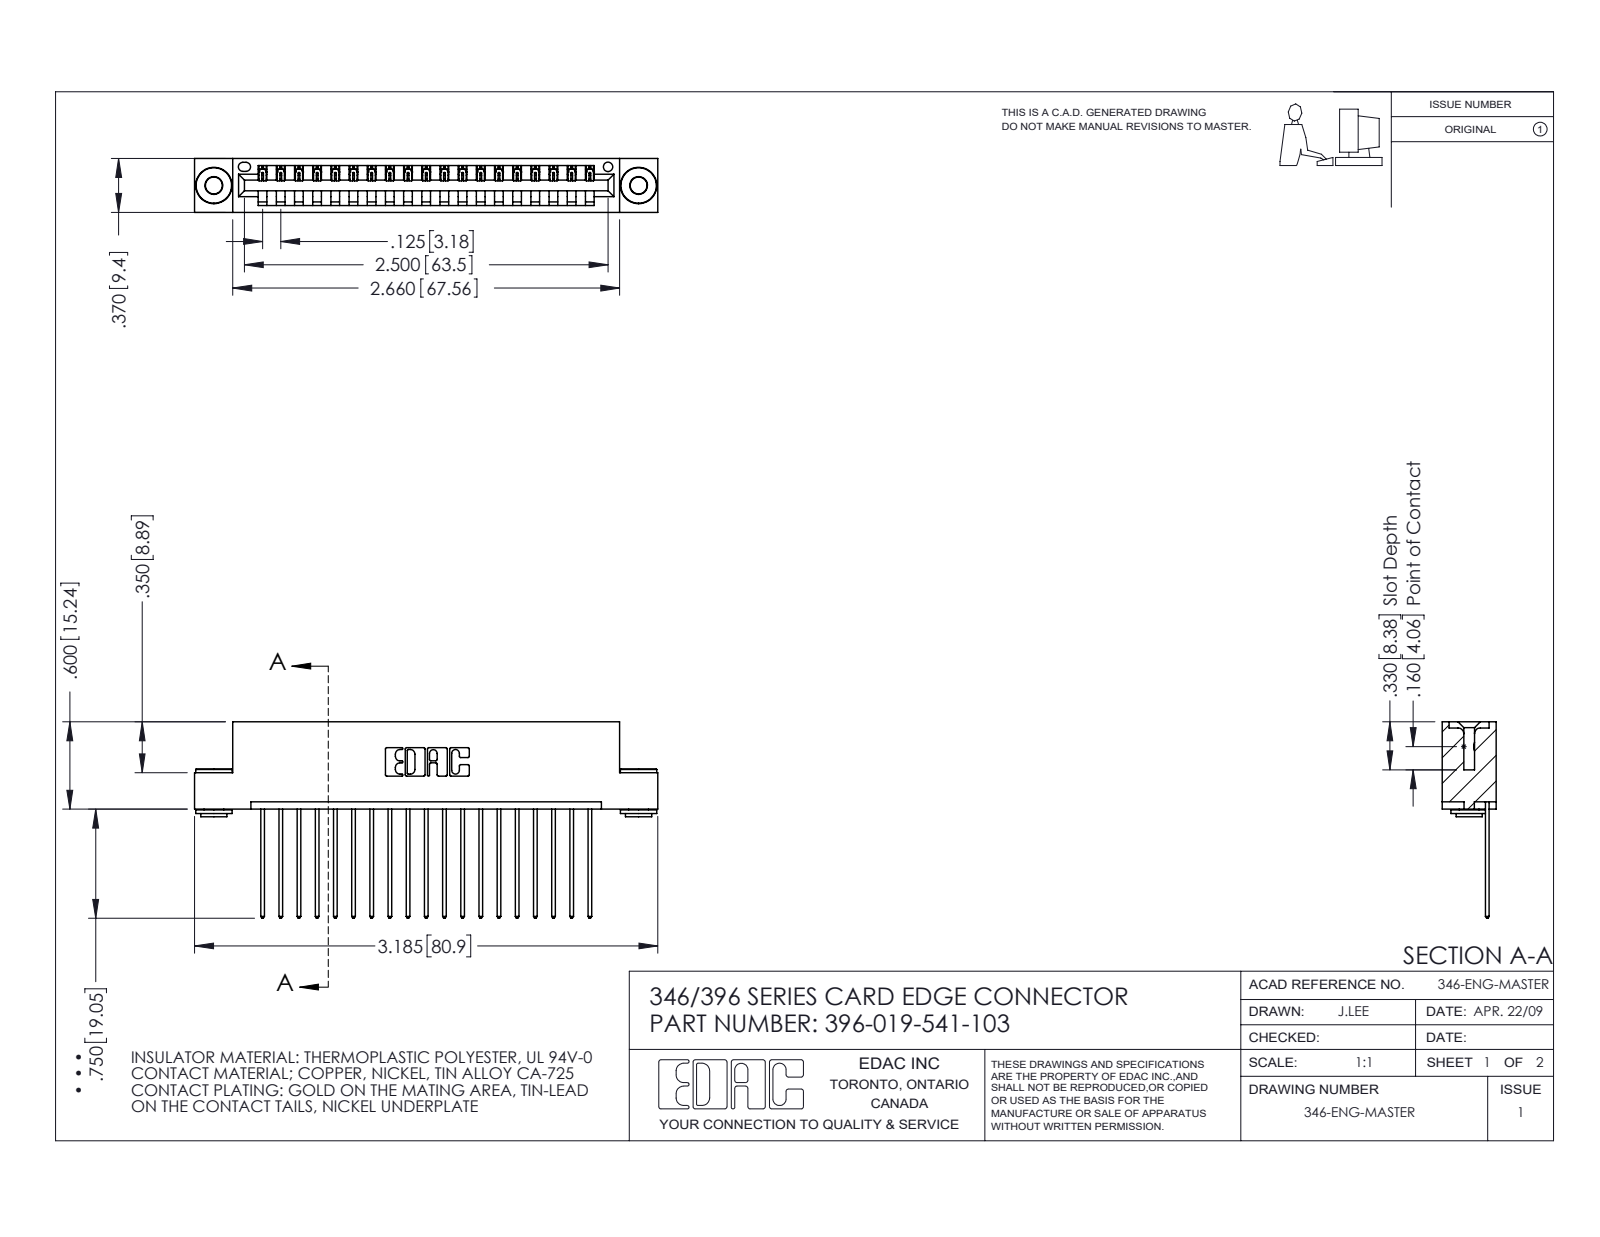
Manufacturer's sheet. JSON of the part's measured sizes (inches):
{"part_name": "345-292-001_345-293-141; 396-019-541-103; 346 Part_Flush Mounting Lugs - 0.156 Dia-TH; 345-250-002_345-250-002-102", "step_written_by": "SolidWorks 2016 (CONFIG_CONTROL_DESIGN)", "units": "inches", "bodies": {"solids": 22, "faces": 1262, "planar": 846, "cylindrical": 408, "other": 8}, "overall_size": [3.185, 1.35, 0.37], "volume_in3": 0.468, "surface_area_in2": 15.39, "round_holes": [[0.116, 2], [0.156, 2], [0.064, 1]], "round_bosses_or_shafts": [[0.25, 2], [0.18, 2], [0.136, 2]], "partial_cylinders_radius": [[0.006, 38], [0.01, 38], [0.01, 22], [0.007, 6], [0.031, 6], [0.026, 3], [0.031, 2], [0.04, 2]], "face_to_face_distances": [0.048, 0.322, 0.25, 0.37, 0.025, 0.072, 0.298, 0.148, 0.222, 0.1], "hole_center_spacings": [0.246, 2.713, 2.92]}
